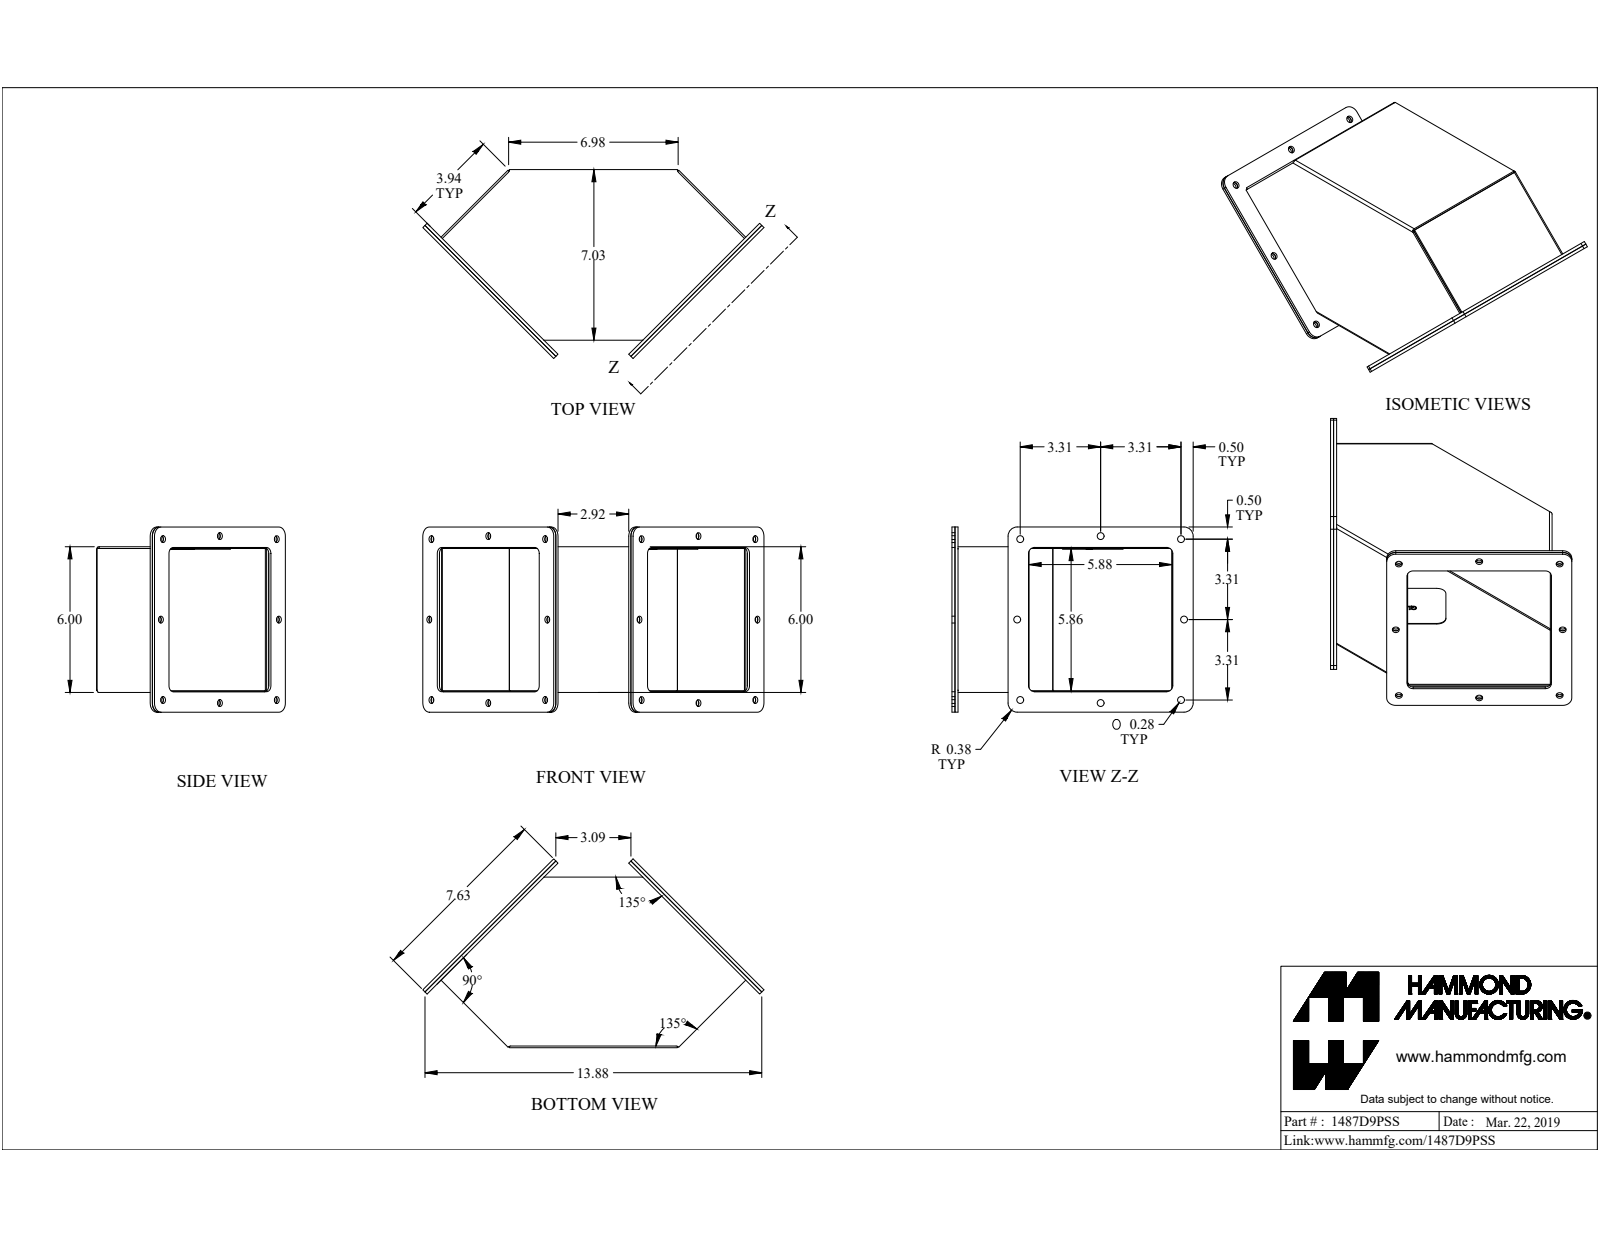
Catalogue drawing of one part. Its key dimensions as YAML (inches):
part_name: "1487D9PSS"
step_written_by: "SolidWorks 2019 (CONFIG_CONTROL_DESIGN)"
units: inches
bodies: {solids: 12, faces: 401, planar: 238, cylindrical: 122, other: 41}
overall_size: [14.053, 7.778, 7.625]
volume: 28.42
surface_area: 706.5
round_holes:
  - {diameter: 0.281, count: 19}
  - {diameter: 0.196, count: 2}
  - {diameter: 0.258, count: 2}
  - {diameter: 0.35, count: 2}
round_bosses_or_shafts:
  - {diameter: 0.5, count: 2}
  - {diameter: 0.25, count: 2}
partial_cylinders:
  - {radius: 0.375, count: 14}
  - {radius: 0.02, count: 12}
  - {radius: 0.25, count: 8}
  - {radius: 0.063, count: 6}
  - {radius: 0.036, count: 5}
  - {radius: 0.108, count: 5}
  - {radius: 0.062, count: 2}
face_to_face_distances: [0.072, 5.928, 5.856, 6, 0.125, 6.954, 8.926, 8.802, 8.998, 8.874]
hole_center_spacings: [3.315, 6.625, 7.519, 9.369, 7.519, 3.315, 4.861, 6.625]
